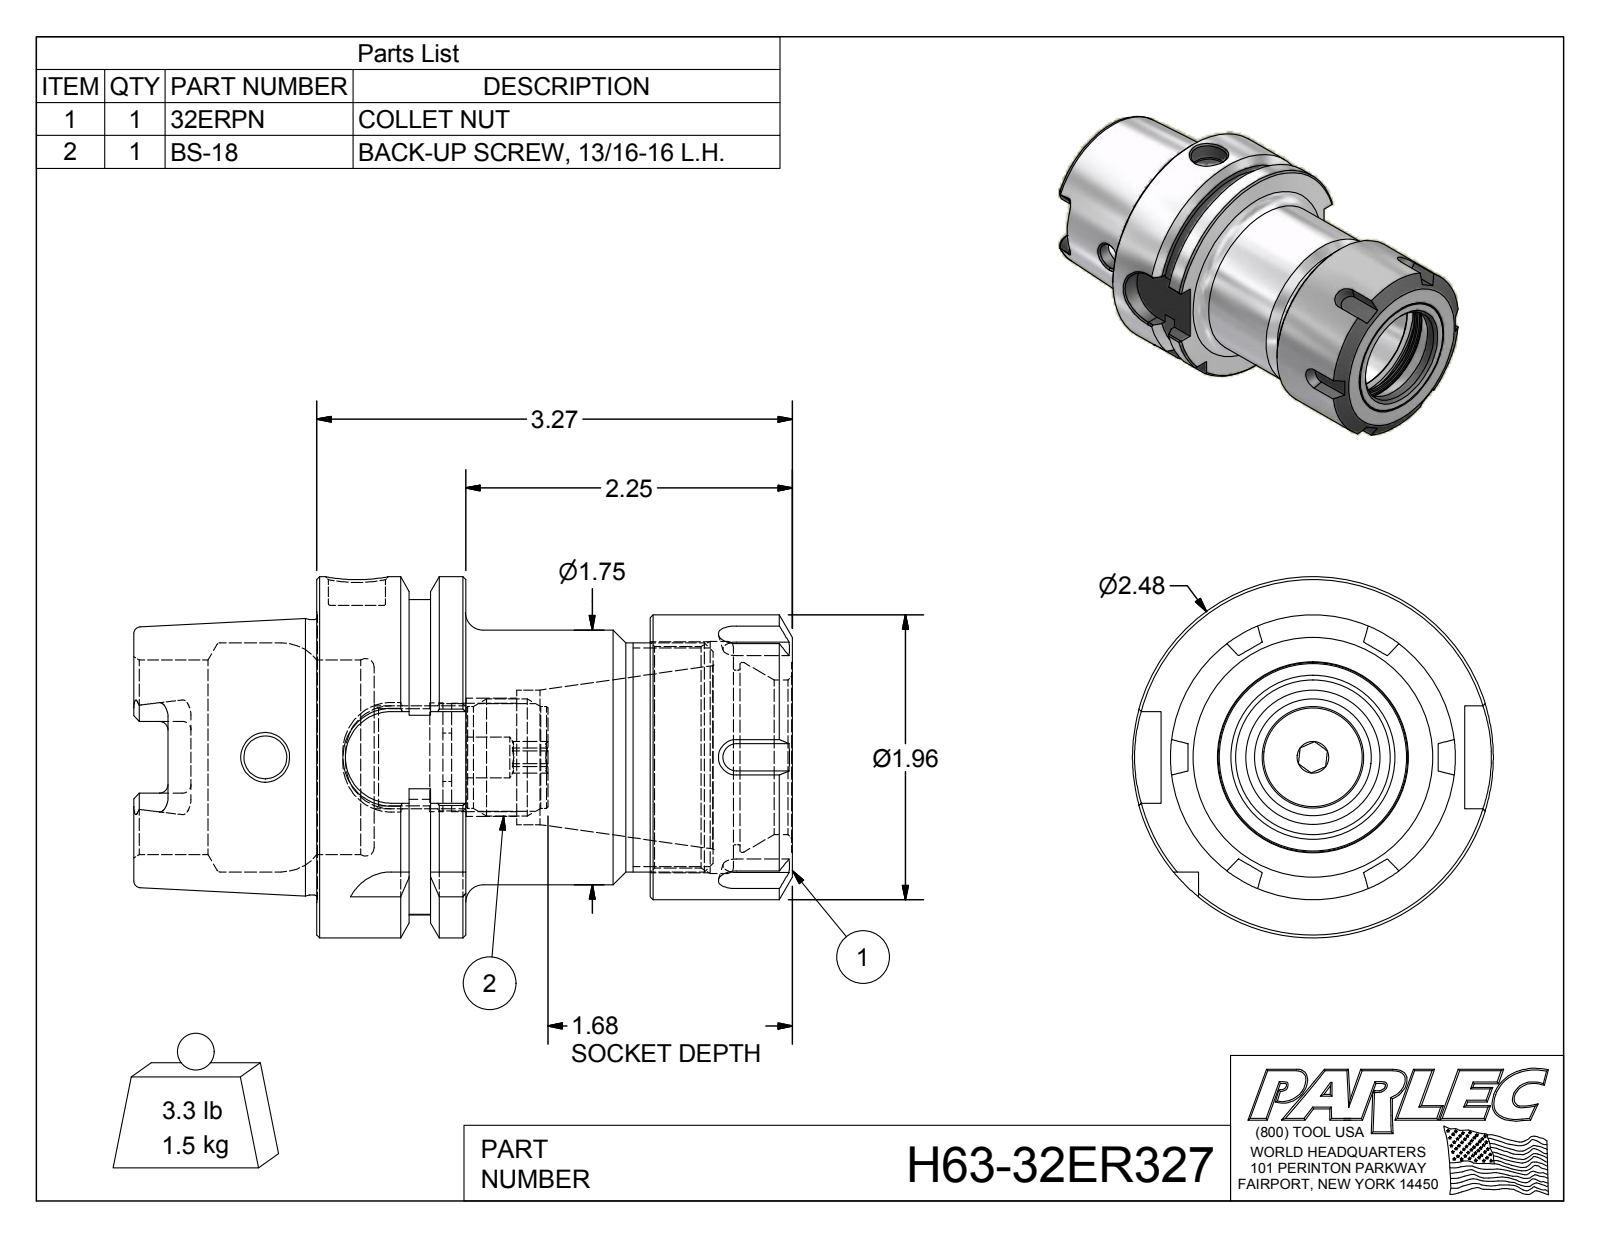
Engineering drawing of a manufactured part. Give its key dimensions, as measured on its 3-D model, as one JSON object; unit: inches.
{"part_name": "H63-32ER327; H63-32ER3-1; BS-18; 32ERPN", "step_written_by": "Autodesk Inventor 2012 (AUTOMOTIVE_DESIGN)", "units": "inches", "bodies": {"solids": 3, "faces": 205, "planar": 84, "cylindrical": 46, "other": 75}, "overall_size": [4.53, 2.48, 2.48], "volume_in3": 8.903, "surface_area_in2": 65.16, "round_holes": [[0.28, 1], [0.295, 1], [0.331, 1], [0.394, 1], [0.666, 1], [0.745, 1], [0.749, 1], [0.925, 1], [1.063, 1], [1.2, 1], [1.305, 1], [1.339, 1]], "round_bosses_or_shafts": [[2.48, 1], [1.958, 1], [1.891, 1], [1.75, 1], [0.805, 1], [0.7, 1]], "partial_cylinders_radius": [[0.059, 6], [0.113, 4], [0.315, 4], [1.083, 1]], "face_to_face_distances": [1.024, 3.27, 2.246, 0.241, 0.389, 2.292, 1.269, 0.978, 0.394, 0.63]}
